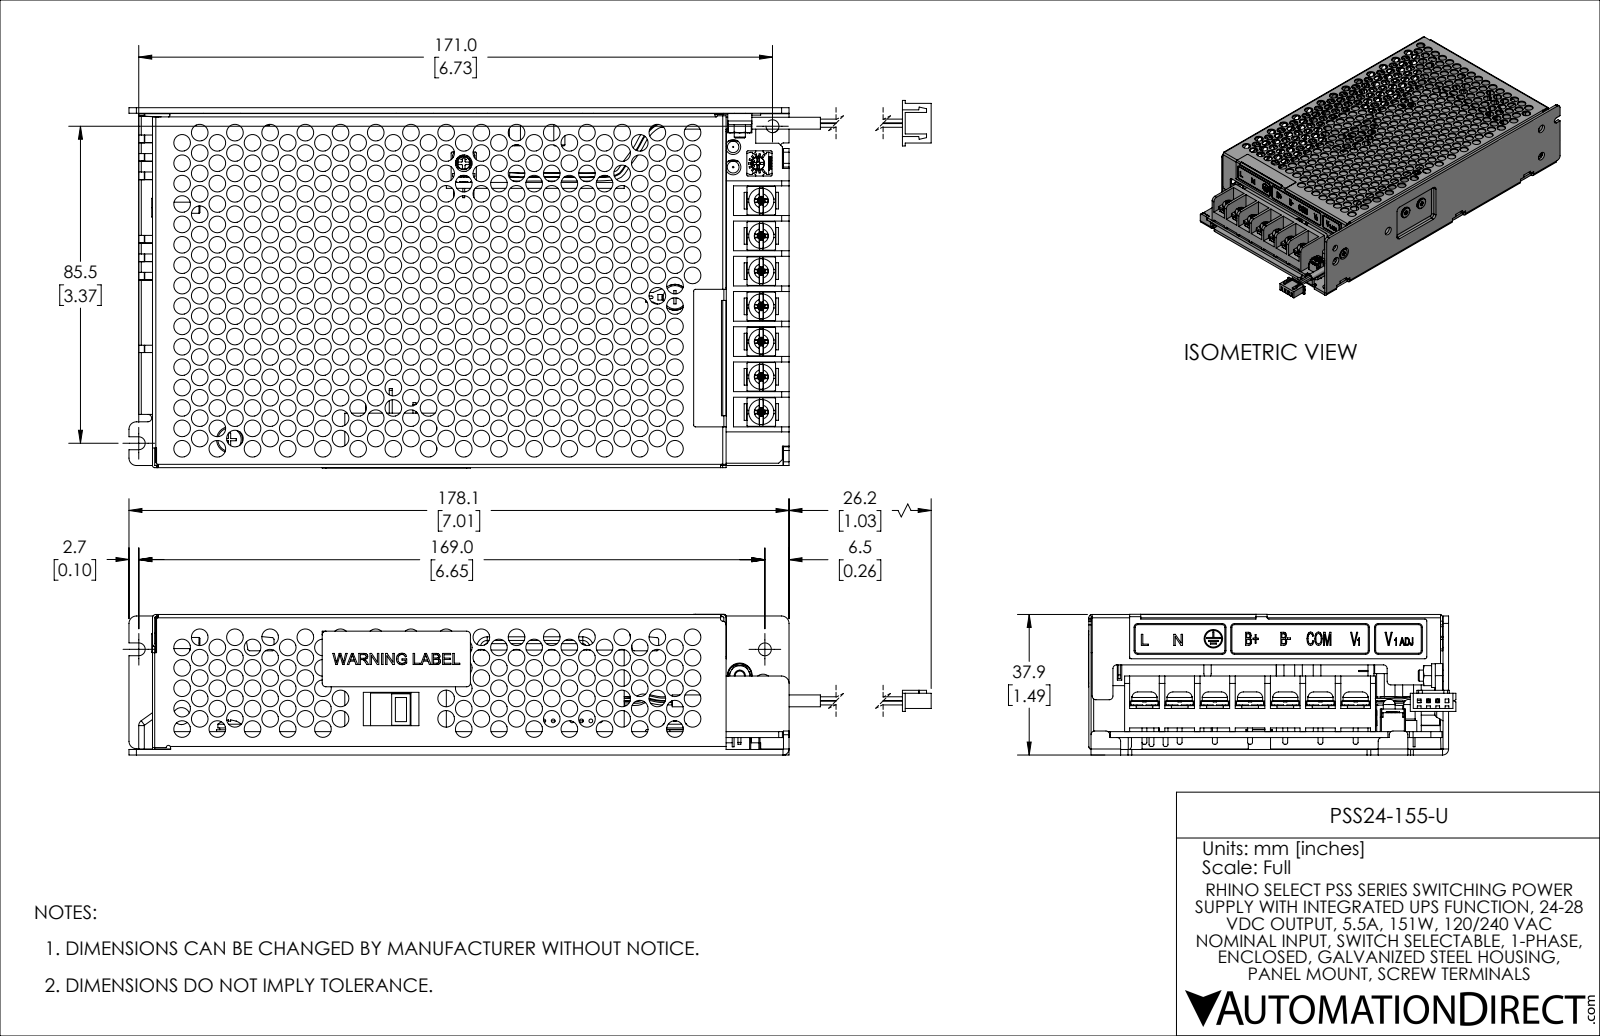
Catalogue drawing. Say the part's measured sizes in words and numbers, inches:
The part is named "PSS12-155-U". Its 3-D file was written by "SolidWorks 2021 (AUTOMOTIVE_DESIGN)". It is 41 solids with 3816 faces: 2218 planar, 1079 cylindrical and 519 other. Overall it measures 8.045 by 3.904 by 1.494 inches. Its volume is 5.493 cubic inches and its surface area 226.8 square inches. Round holes: 610 of diameter 0.177, 14 of diameter 0.118, 7 of diameter 0.04, 4 of diameter 0.181, 3 of diameter 0.138, 2 of diameter 0.107, 2 of diameter 0.142, 1 of diameter 0.106, 1 of diameter 0.126, 1 of diameter 0.126, 1 of diameter 0.128, 1 of diameter 0.137. Round bosses or shafts: 9 of diameter 0.197, 9 of diameter 0.157, 7 of diameter 0.268, 4 of diameter 0.236, 4 of diameter 0.134, 4 of diameter 0.039, 3 of diameter 0.209, 3 of diameter 0.118. Partial cylindrical surfaces (rounded edges, fillets, slot ends): 59 of radius 0.039, 56 of radius 0.02, 39 of radius 0.004, 38 of radius 0.012, 36 of radius 0.008, 15 of radius 0.028, 12 of radius 0.079, 5 of radius 0.005. The main face-to-face distances are 0.059, 0.063, 0.248, 0.189, 0.185, 0.126, 0.024, 1.493, 1.433, 1.307. The hole center spacings are 0.432, 0.217, 0.572, 0.433, 0.75, 0.374, 0.65, 0.943.
